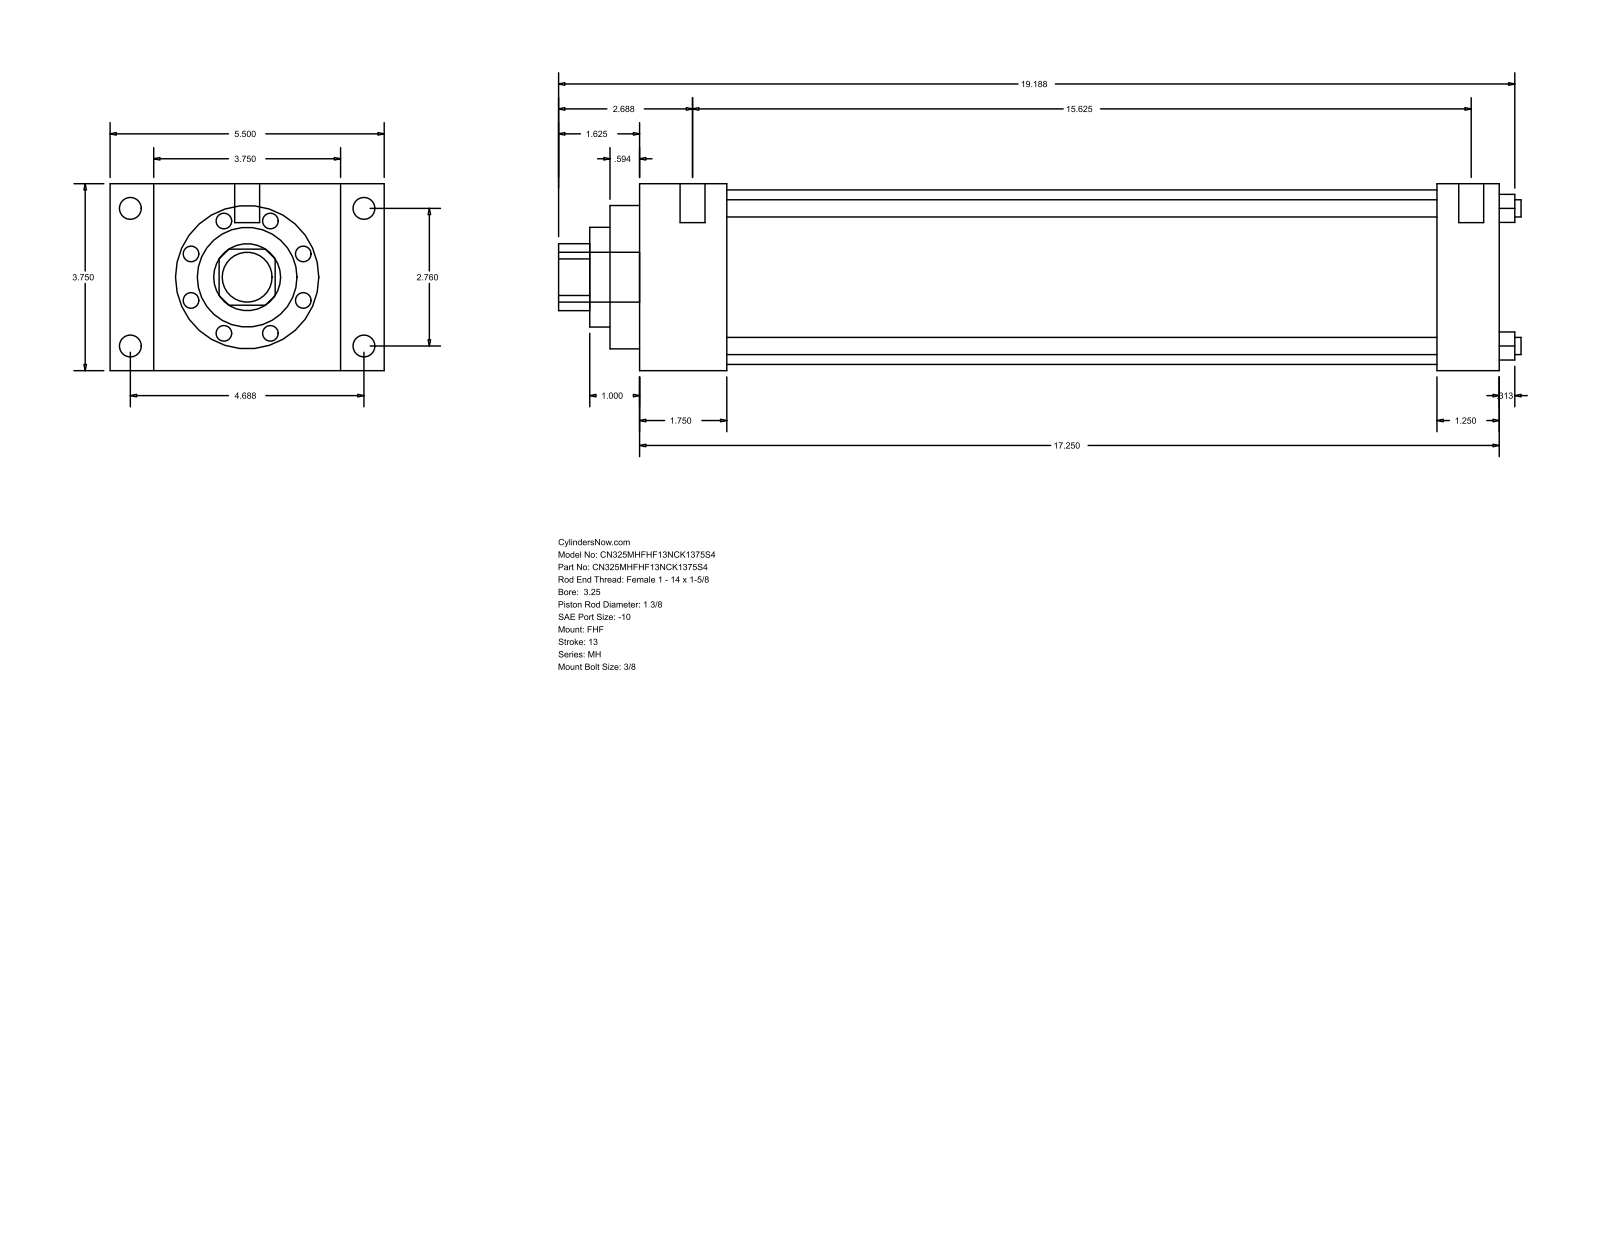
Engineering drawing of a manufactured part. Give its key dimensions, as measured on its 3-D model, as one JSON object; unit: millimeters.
{"part_name": "MH_FHF__0325_1.375", "step_written_by": "GSSL Pune (CONFIG_CONTROL_DESIGN)", "units": "millimeters", "bodies": {"solids": 0, "faces": 90, "planar": 61, "cylindrical": 29, "other": 0}, "overall_size": [490.54, 139.7, 95.25], "round_holes": [[8.76, 4], [34.92, 1], [50.8, 1], [73.03, 1], [88.9, 1]], "round_bosses_or_shafts": [[11.13, 4], [5.56, 4], [12.7, 2], [25.4, 1]], "partial_cylinders_radius": [[17.06, 1]], "face_to_face_distances": [95.24, 438.16, 44.45, 393.71, 22.23, 117.47, 139.7, 406.41, 361.96, 31.75], "hole_center_spacings": [49.57, 70.1, 99.14]}
